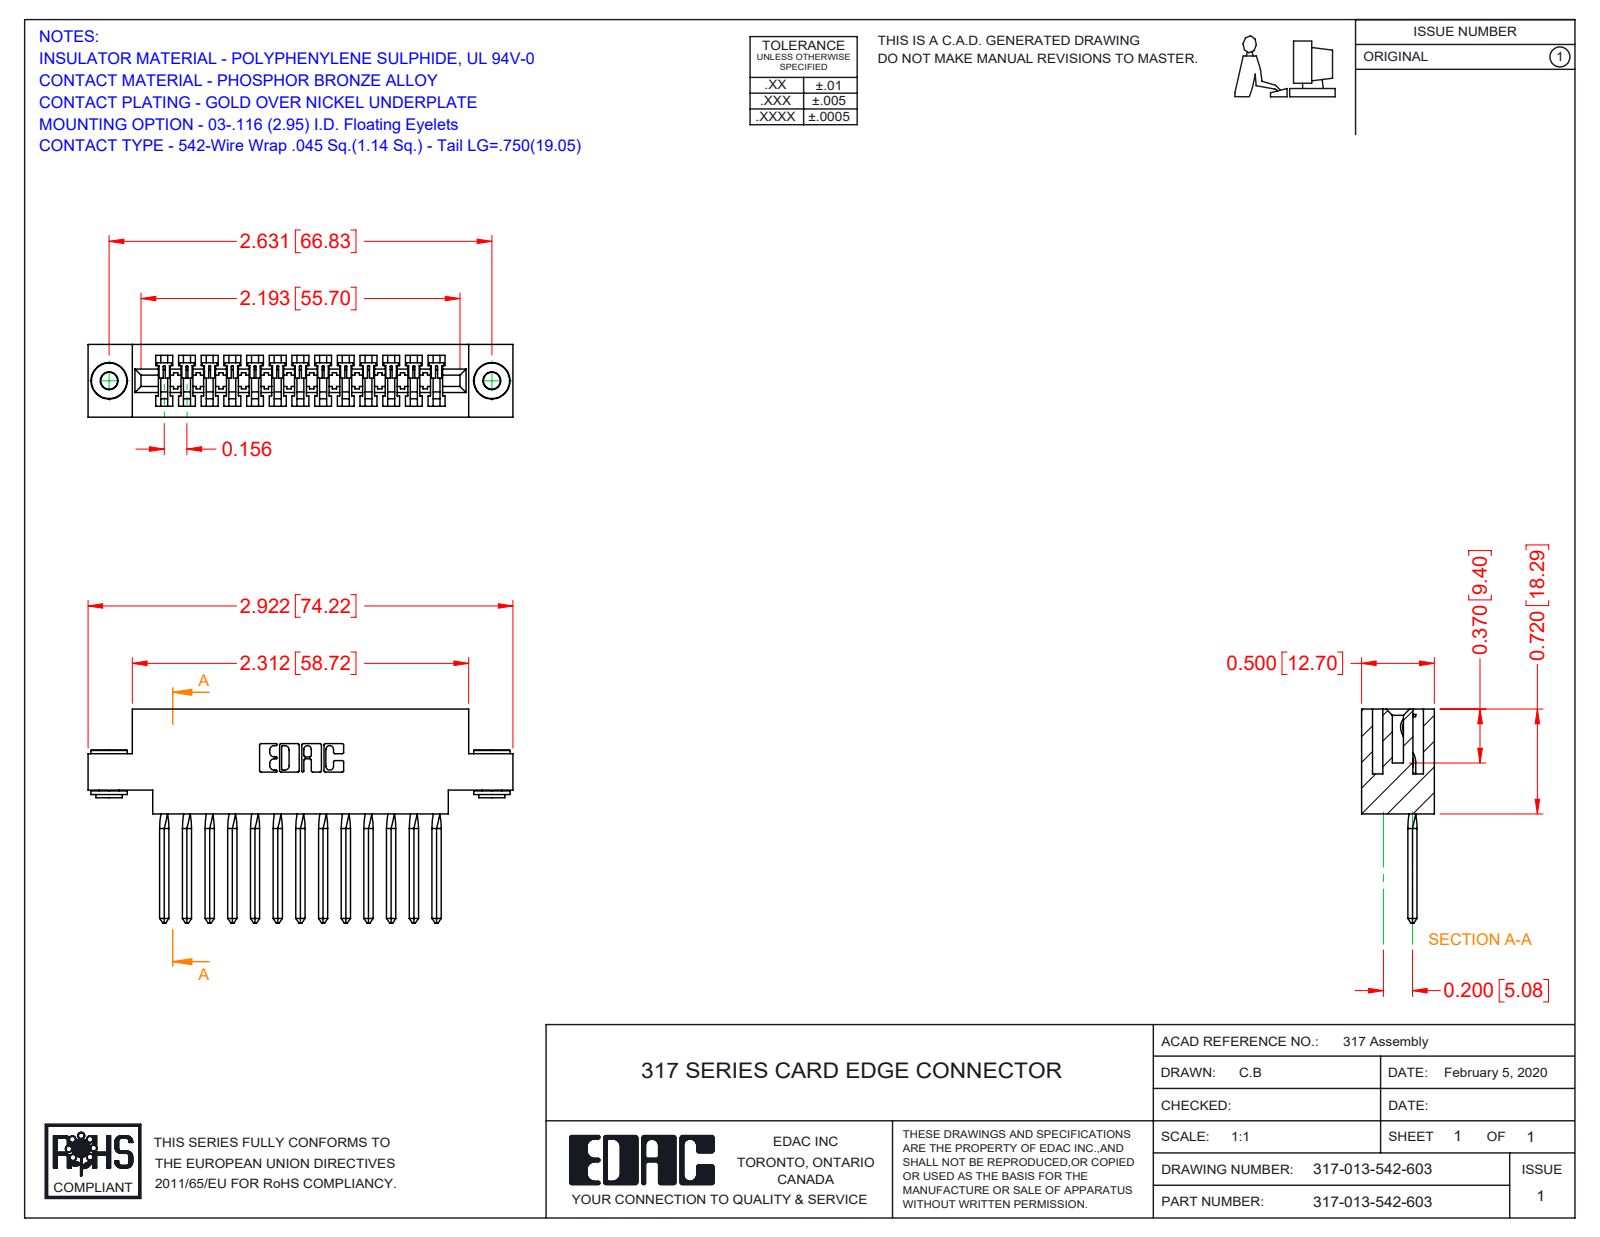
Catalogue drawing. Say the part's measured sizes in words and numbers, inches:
The part is named "317-290-003_542; 317-013-542-603; 345-250-002_345-250-002-102; 317 Part_.156 Dia - TH". Its 3-D file was written by "SolidWorks 2016 (CONFIG_CONTROL_DESIGN)". It is 16 solids with 1115 faces: 900 planar, 155 cylindrical and 60 other. Overall it measures 2.922 by 1.47 by 0.5 inches. Its volume is 0.654 cubic inches and its surface area 19.59 square inches. Round holes: 2 of diameter 0.116, 2 of diameter 0.156. Round bosses or shafts: 2 of diameter 0.25, 2 of diameter 0.18, 2 of diameter 0.136. Partial cylindrical surfaces (rounded edges, fillets, slot ends): 26 of radius 0.006, 22 of radius 0.01, 6 of radius 0.007, 6 of radius 0.031, 3 of radius 0.026, 1 of radius 0.074, 1 of radius 0.089, 1 of radius 0.1. The main face-to-face distances are 0.5, 0.075, 0.425, 0.11, 0.065, 0.35, 0.22, 0.136, 0.305, 0.72. The hole center spacings are 2.631.
